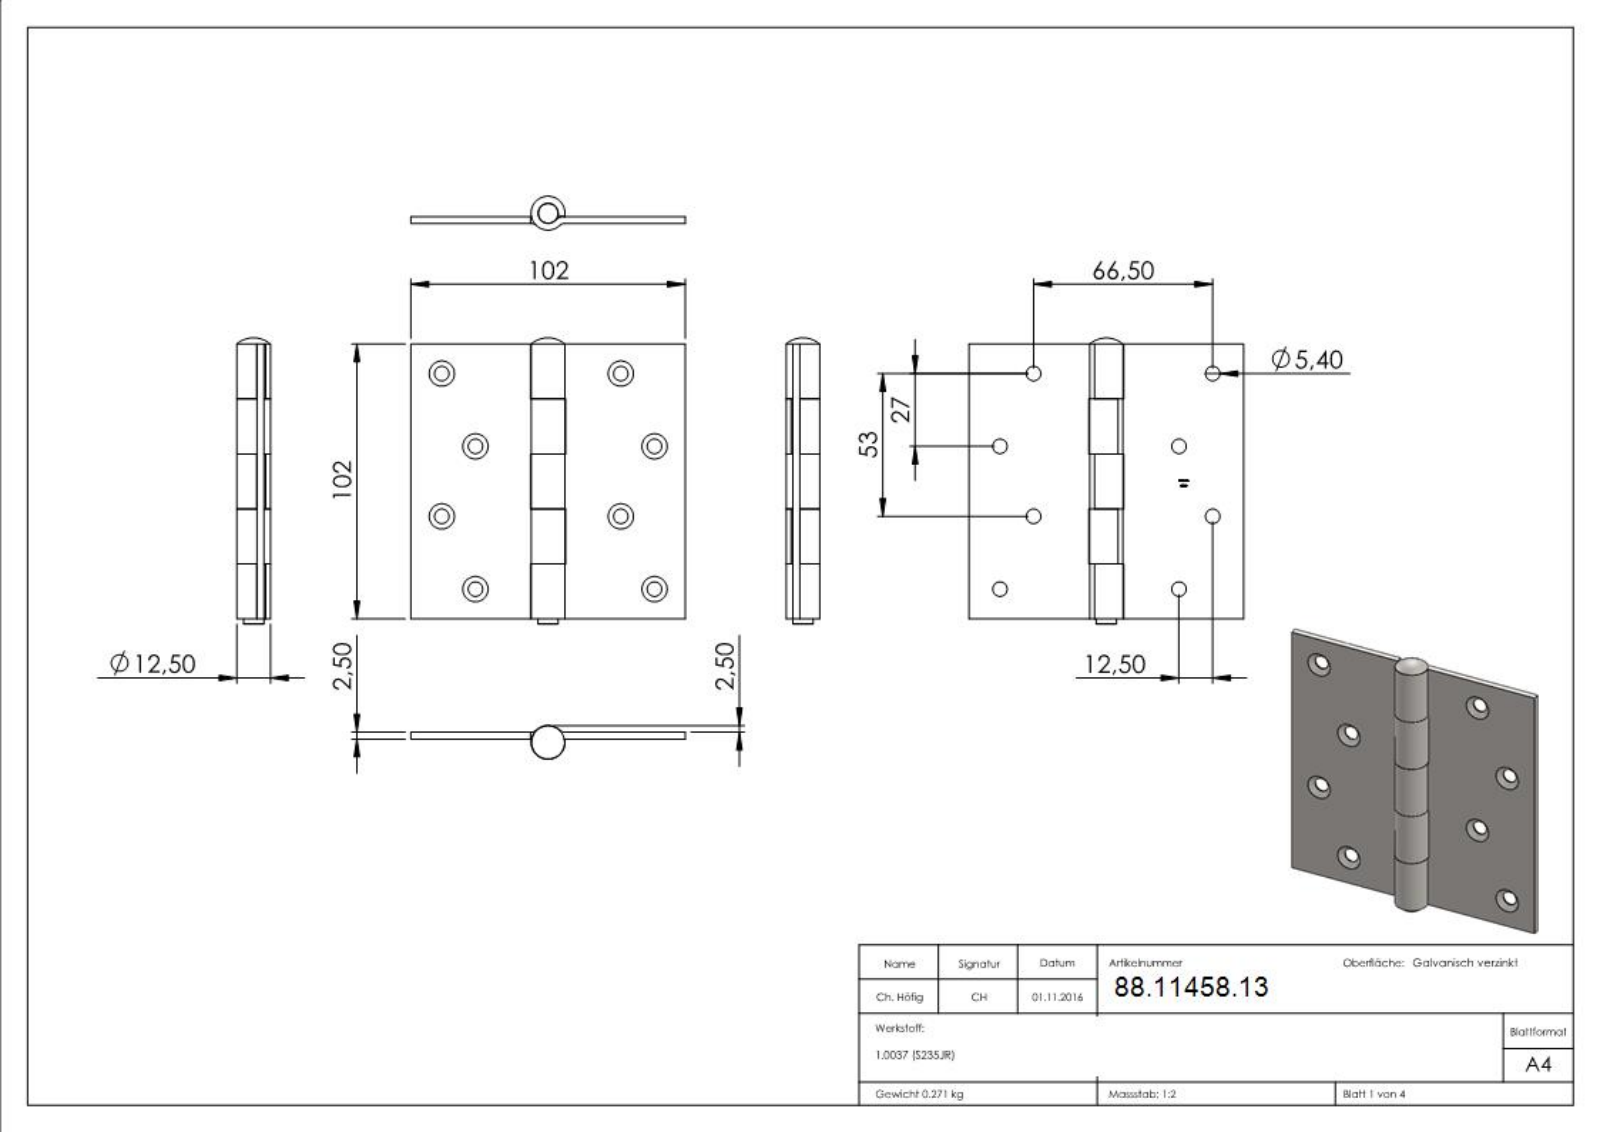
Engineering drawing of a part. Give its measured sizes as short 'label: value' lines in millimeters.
name: 458-13 Teil3; 458-13 Teil2; 458-13; 458-13 Teil1
written by: SolidWorks 2018 (CONFIG_CONTROL_DESIGN)
unit: mm
bodies: 3 solids, 262 faces (136 planar, 29 cylindrical, 97 other)
size: 106.2 × 102 × 12.5
volume: 34 699 mm³; area: 29 429 mm²
holes: 8× ⌀5.4, 1× ⌀7.5
bosses: 1× ⌀12.5
rounds: 2× R2.5, 2× R5
face distances: 2.5, 20.4, 40.8, 102, 61.2, 81.6, 44.5, 57.5, 13, 2
hole spacings: 29.75, 53, 66.5, 85.04, 28.85, 60.37, 80.97, 83.49
